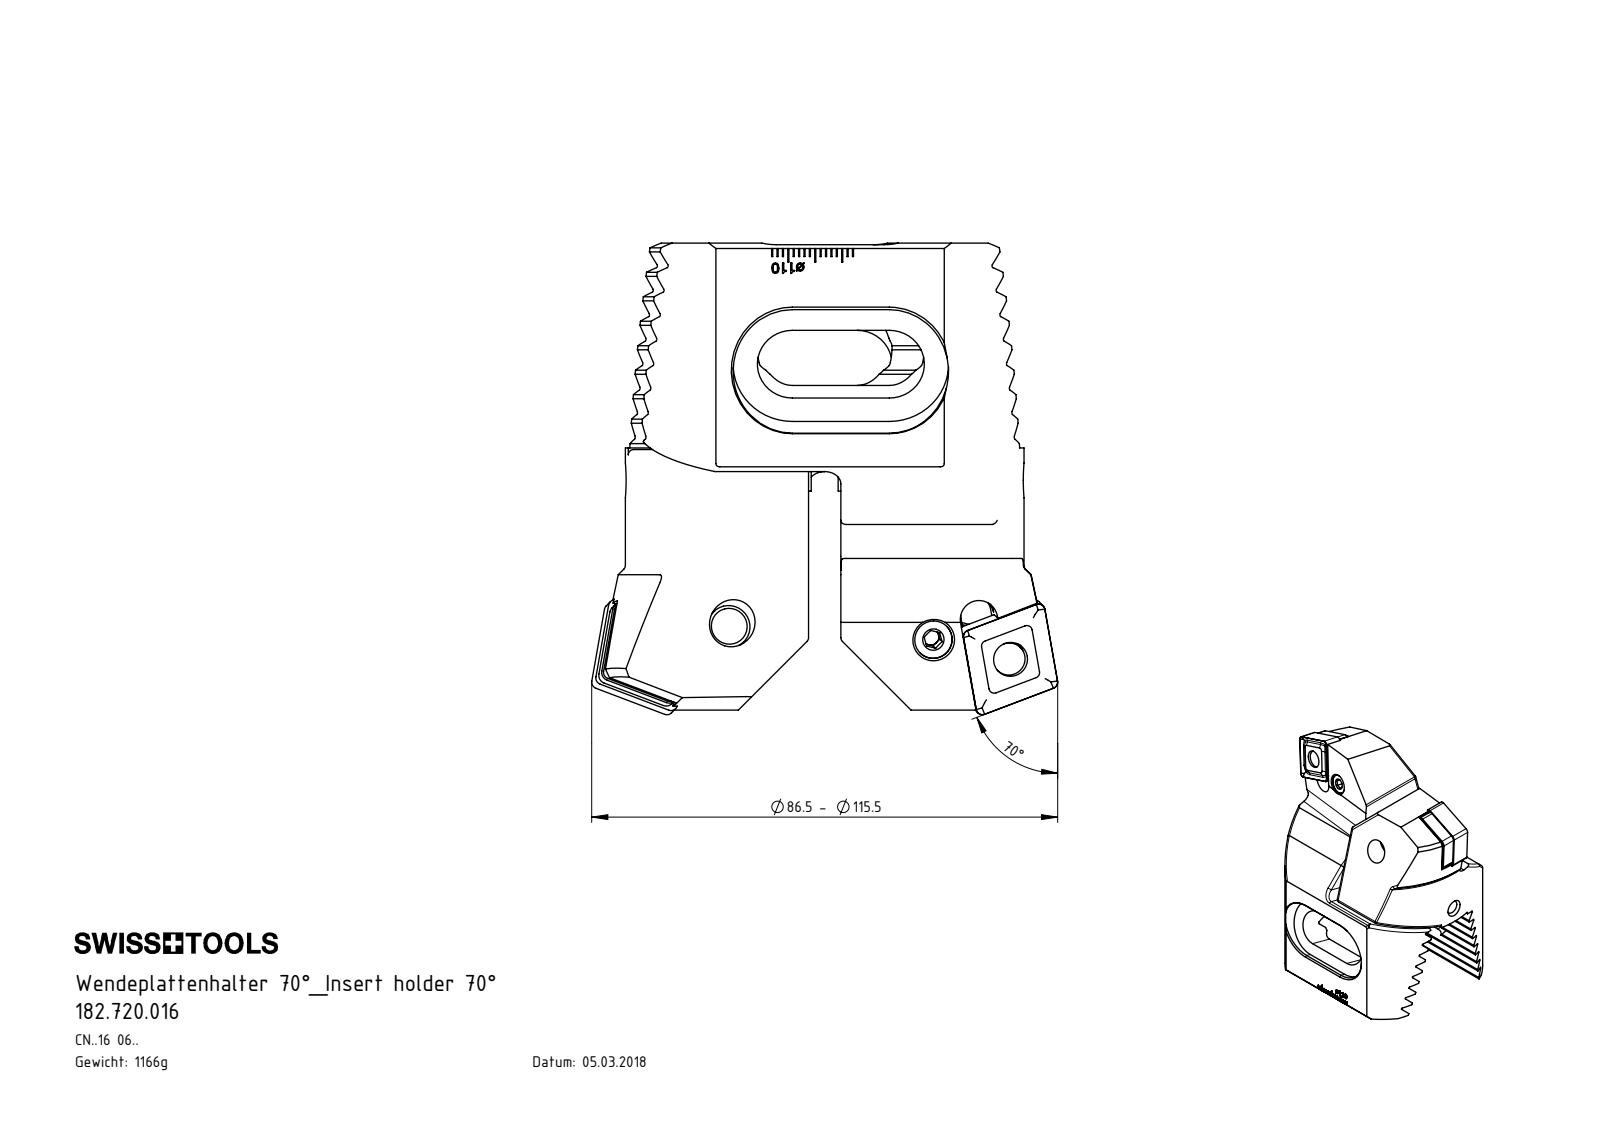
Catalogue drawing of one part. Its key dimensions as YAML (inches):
part_name: "182.720.016; Z72-ER3.001.030; CNMG160612; WCE-ER2.101.004_A (+5 more)"
step_written_by: "SolidWorks 2017 (CONFIG_CONTROL_DESIGN)"
units: inches
bodies: {solids: 14, faces: 902, planar: 486, cylindrical: 172, other: 244}
overall_size: [3.445, 3.406, 2.291]
volume: 9.009
surface_area: 67.97
round_holes:
  - {diameter: 0.079, count: 2}
  - {diameter: 0.25, count: 2}
  - {diameter: 0.276, count: 2}
  - {diameter: 0.317, count: 2}
  - {diameter: 0.331, count: 2}
  - {diameter: 0.197, count: 1}
round_bosses_or_shafts:
  - {diameter: 0.236, count: 3}
  - {diameter: 0.315, count: 2}
  - {diameter: 0.311, count: 2}
  - {diameter: 0.252, count: 2}
  - {diameter: 0.14, count: 2}
  - {diameter: 0.157, count: 1}
partial_cylinders:
  - {radius: 0.013, count: 16}
  - {radius: 0.039, count: 16}
  - {radius: 0.047, count: 8}
  - {radius: 0.059, count: 8}
  - {radius: 0.118, count: 6}
  - {radius: 0.138, count: 6}
  - {radius: 0.012, count: 4}
  - {radius: 0.256, count: 4}
face_to_face_distances: [0.16, 0.32, 0.802, 0.481, 0.641, 0.801, 0.962, 0.236, 0.063, 2.291]
hole_center_spacings: [0.582, 0.591, 0.787, 1.521]
